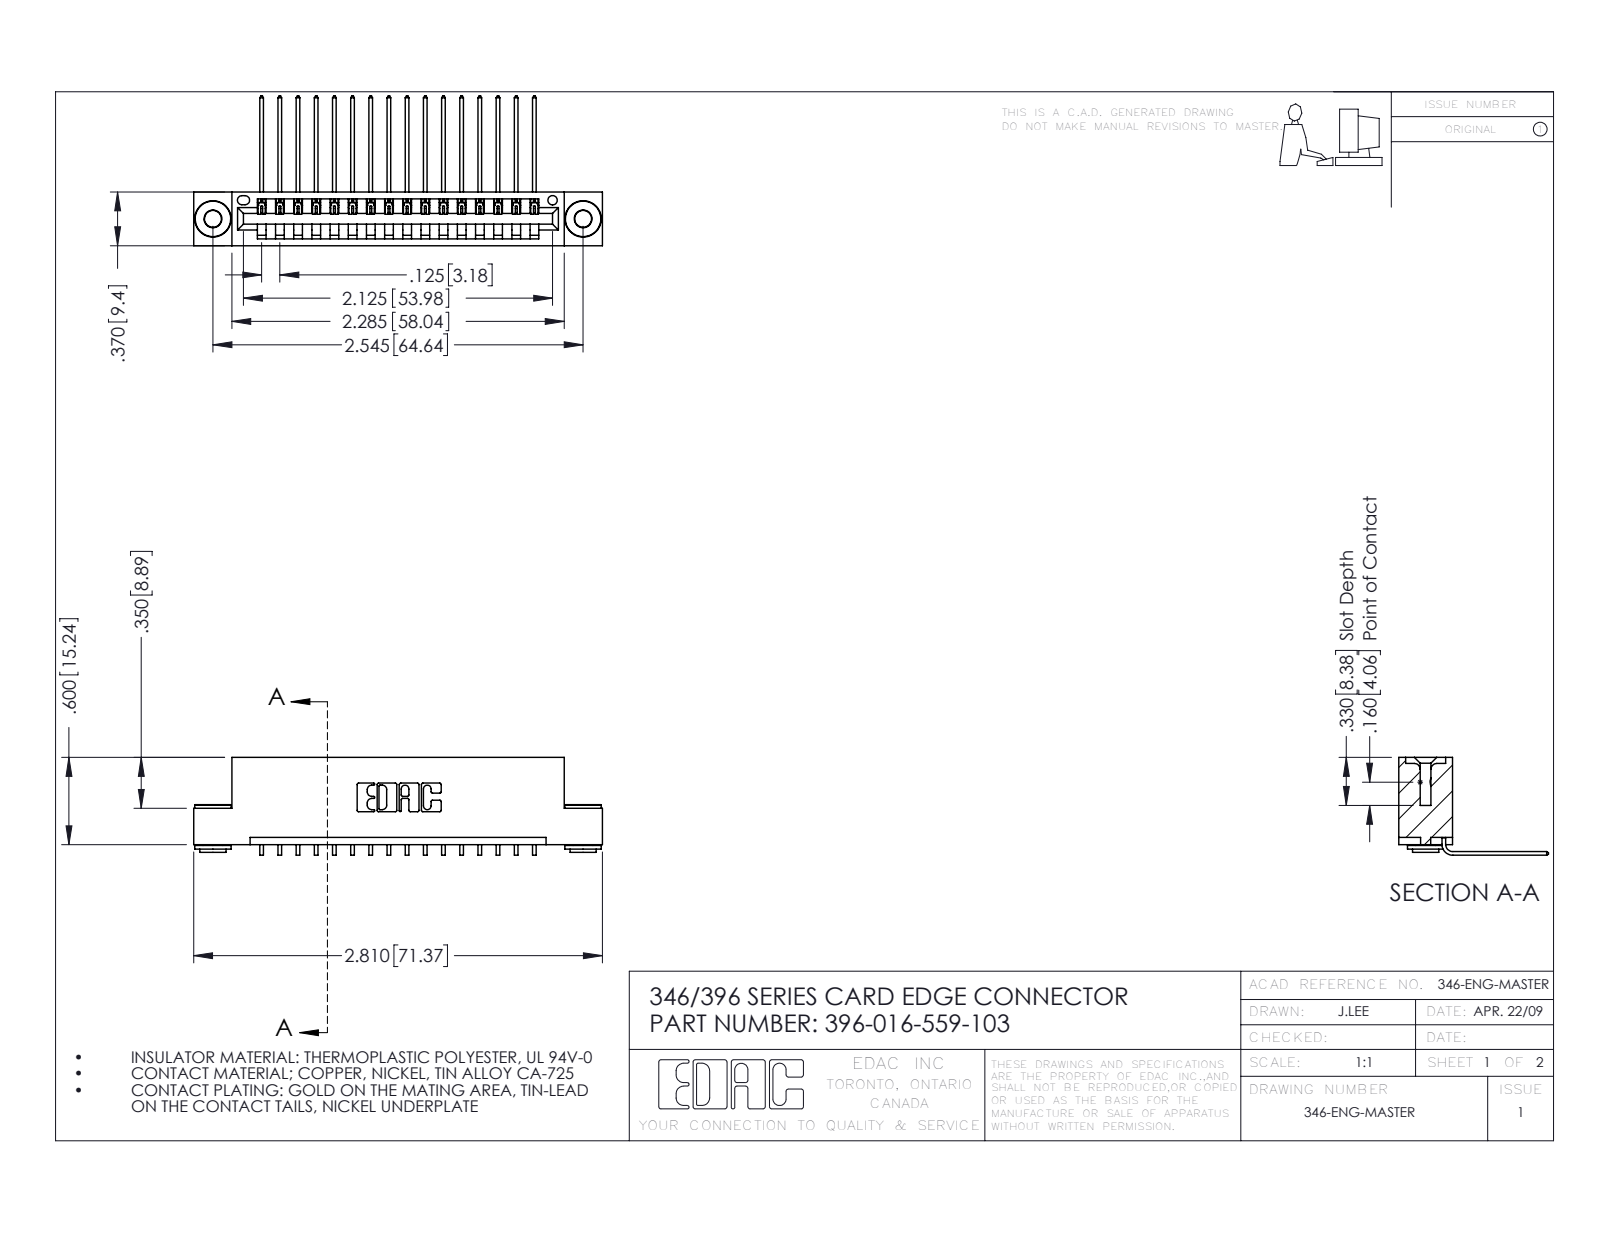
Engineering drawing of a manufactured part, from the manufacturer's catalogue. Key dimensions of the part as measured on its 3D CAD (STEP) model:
Part name (STEP PRODUCT): 396-016-559-103; 345-250-002_345-250-002-102; 346 Part_Flush Mounting Lugs - 0.156 Dia-TH; 345-292-001_558 559 Tail - 1
STEP written by: SolidWorks 2016 (CONFIG_CONTROL_DESIGN)
Units: inches
Bodies: 19 solids, 1120 faces (758 planar, 354 cylindrical, 8 other)
Overall size (bounding box): 2.81 × 1.03 × 0.673
Volume: 0.41 in³ · Surface area: 13.43 in²
Round holes (diameter × count): ⌀0.116 ×2, ⌀0.156 ×2, ⌀0.064 ×1
Round bosses / shafts (diameter × count): ⌀0.25 ×2, ⌀0.18 ×2, ⌀0.136 ×2
Partial cylindrical surfaces — rounded edges, fillets, slot ends (radius × count): R0.006 ×32, R0.01 ×22, R0.007 ×6, R0.031 ×6, R0.026 ×3, R0.031 ×2, R0.04 ×2, R0.014 ×1
Main face-to-face distances: 0.048, 0.322, 0.25, 0.37, 0.025, 0.072, 0.298, 0.148, 0.222, 0.1
Hole centre spacings: 0.246, 2.338, 2.545
